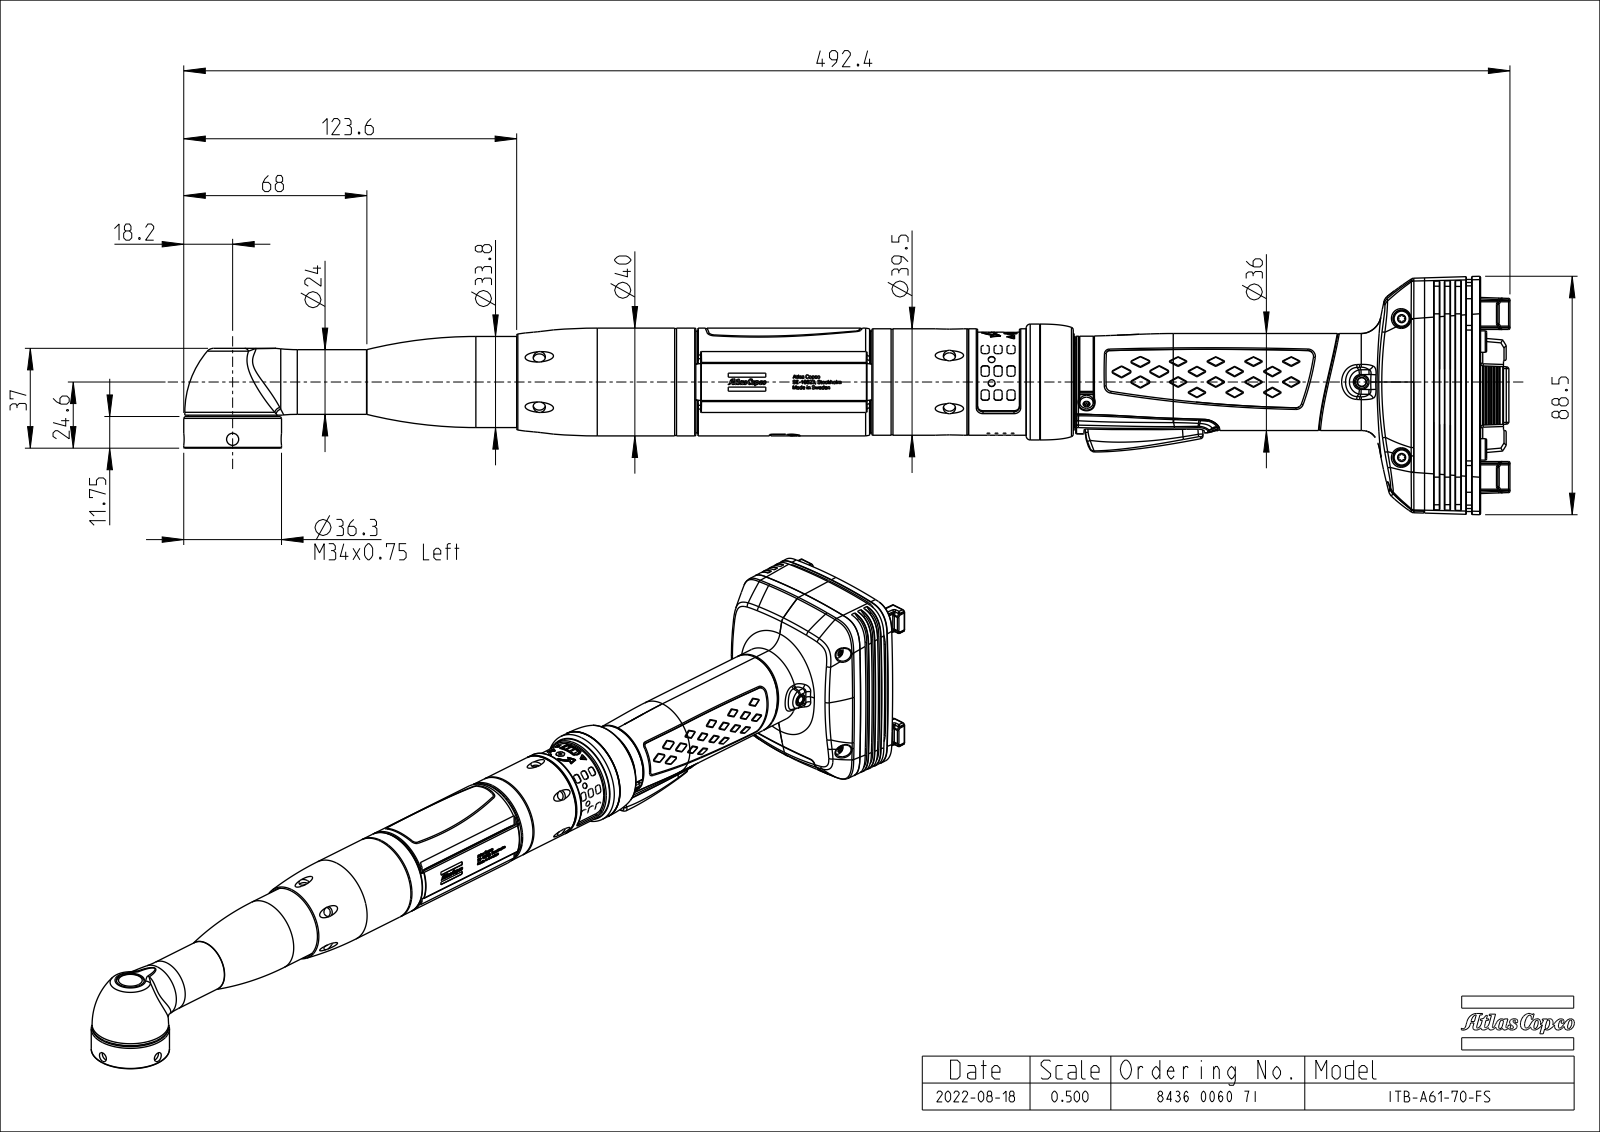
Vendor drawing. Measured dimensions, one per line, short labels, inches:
name: EXT_COMP_SW0001
written by: CREO PARAMETRIC BY PTC INC, 2020281 (CONFIG_CONTROL_DESIGN)
unit: in
bodies: 5 solids, 11415 faces (4131 planar, 2450 cylindrical, 4834 other)
size: 19.384 × 3.484 × 2.934
volume: 27.27 in³; area: 274.6 in²
holes: 12× ⌀0.039, 9× ⌀0.177, 7× ⌀0.118, 6× ⌀0.098, 6× ⌀0.126, 4× ⌀0.087, 4× ⌀0.13, 4× ⌀0.169, 4× ⌀0.228, 4× ⌀0.256, 3× ⌀0.157, 2× ⌀0.063
bosses: 4× ⌀0.244, 4× ⌀0.217, 4× ⌀0.157, 2× ⌀0.22, 2× ⌀0.197, 2× ⌀0.118, 2× ⌀0.098, 1× ⌀1.693
rounds: 527× R0.012, 226× R0.02, 217× R0.008, 87× R0.079, 86× R0.039, 32× R0.004, 25× R0.118, 24× R0.011
face distances: 0.098, 0.199, 0.795, 0.874, 0.697, 1.346, 0.331, 0.091, 0.087, 0.441
hole spacings: 0.118, 0.236, 0.75, 2.184, 2.294, 3.077, 0.354, 5.994
